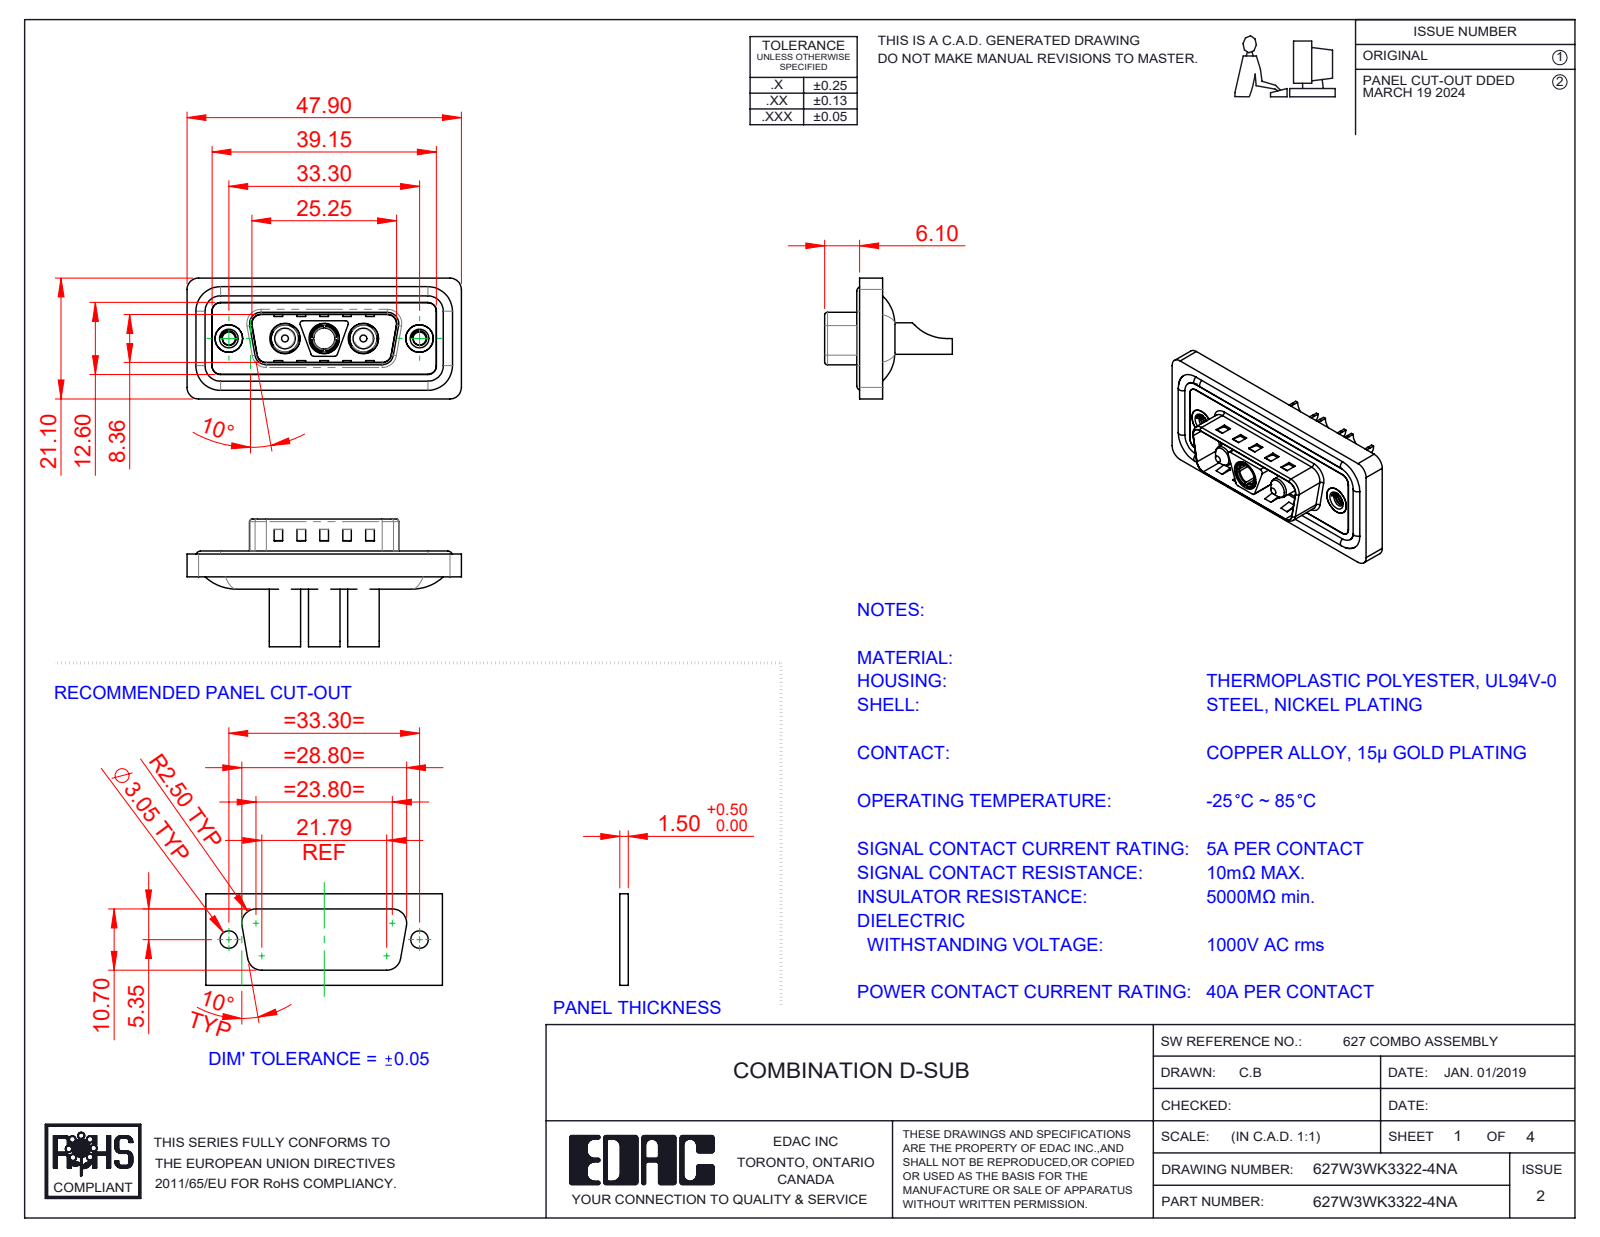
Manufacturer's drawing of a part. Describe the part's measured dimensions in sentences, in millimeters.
The part is named "627W3WK3322-4NA; 627Combo Shell Rear_15 Contacts; 627Combo Waterproof Housing_15 Contacts; 627Combo Shell Front_15 Contacts (+4 more)". Its 3-D file was written by "SolidWorks 2023 (CONFIG_CONTROL_DESIGN)". It is 13 solids with 619 faces: 237 planar, 255 cylindrical and 127 other. Overall it measures 47.9 by 22.3 by 21.1 millimeters. Its volume is 5 809 cubic millimeters and its surface area 9 544 square millimeters. Round holes: 3 of diameter 4.6, 3 of diameter 4.85, 3 of diameter 5.3, 2 of diameter 2.26, 2 of diameter 4, 2 of diameter 4.8, 2 of diameter 5, 1 of diameter 3.7. Round bosses or shafts: 4 of diameter 1.6, 3 of diameter 5.5, 3 of diameter 5.2, 3 of diameter 4.75, 3 of diameter 3.75, 2 of diameter 4.9, 2 of diameter 3.6, 1 of diameter 4.96. Partial cylindrical surfaces (rounded edges, fillets, slot ends): 26 of radius 1.5, 20 of radius 2, 12 of radius 0.5, 8 of radius 1.6, 4 of radius 0.25, 4 of radius 0.6, 4 of radius 0.65, 4 of radius 0.9. The main face-to-face distances are 0.4, 1.1, 0.5, 1.6, 3.1, 2.9, 1.5, 0.82, 9.58, 2.5. The hole center spacings are 6.85, 9.8, 16.65, 23.5, 13.7, 33.3.
